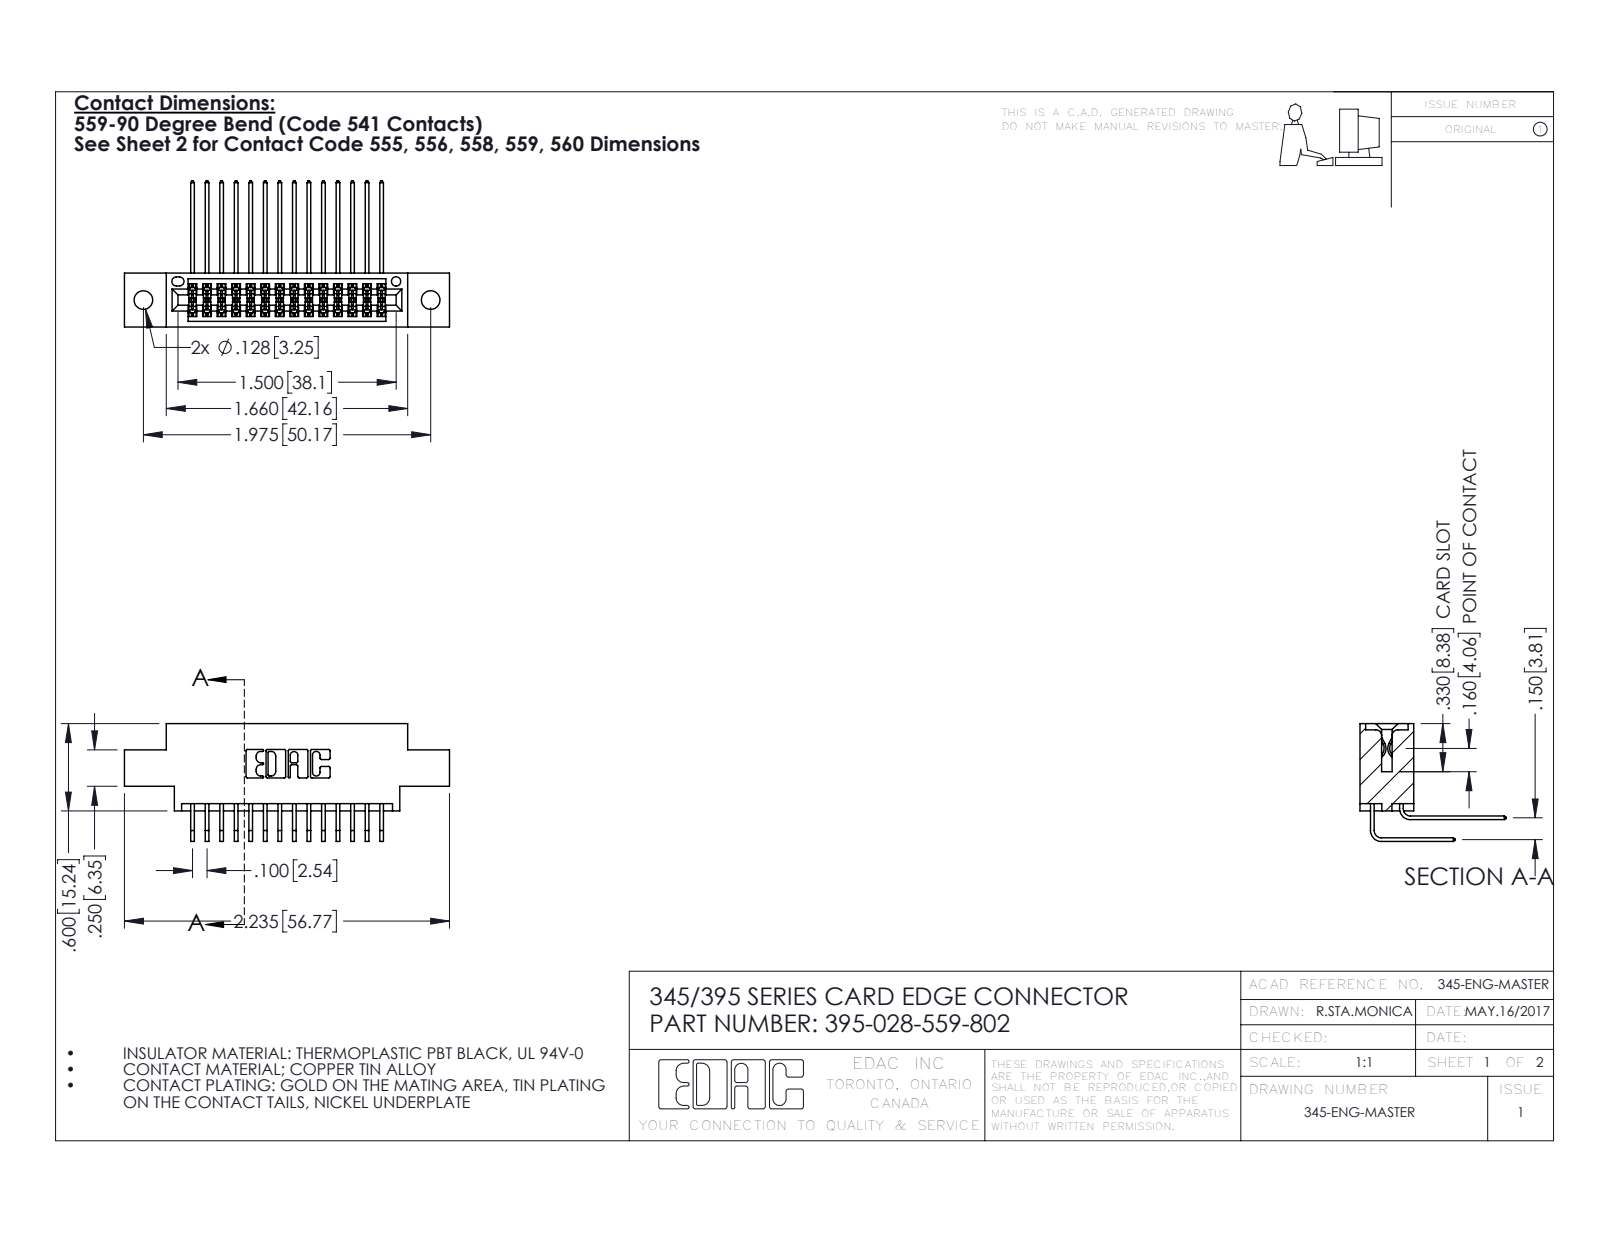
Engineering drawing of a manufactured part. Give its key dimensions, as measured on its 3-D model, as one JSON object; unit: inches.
{"part_name": "345-292-001_559 Tail - 2; 345-292-001_558 559 Tail - 1; 395-028-559-802; 345 Part_0.170 Offset - 0.128 Dia", "step_written_by": "SolidWorks 2016 (CONFIG_CONTROL_DESIGN)", "units": "inches", "bodies": {"solids": 29, "faces": 1586, "planar": 1064, "cylindrical": 522, "other": 0}, "overall_size": [2.235, 1.005, 0.809], "volume_in3": 0.321, "surface_area_in2": 12.2, "round_holes": [[0.128, 2], [0.064, 1]], "partial_cylinders_radius": [[0.006, 42], [0.01, 22], [0.007, 6], [0.031, 6], [0.026, 3], [0.014, 2], [0.019, 2], [0.022, 2]], "face_to_face_distances": [0.072, 0.298, 0.37, 0.2, 0.098, 0.272, 0.025, 0.15, 0.225, 0.175], "hole_center_spacings": [0.27, 1.742, 1.975]}
